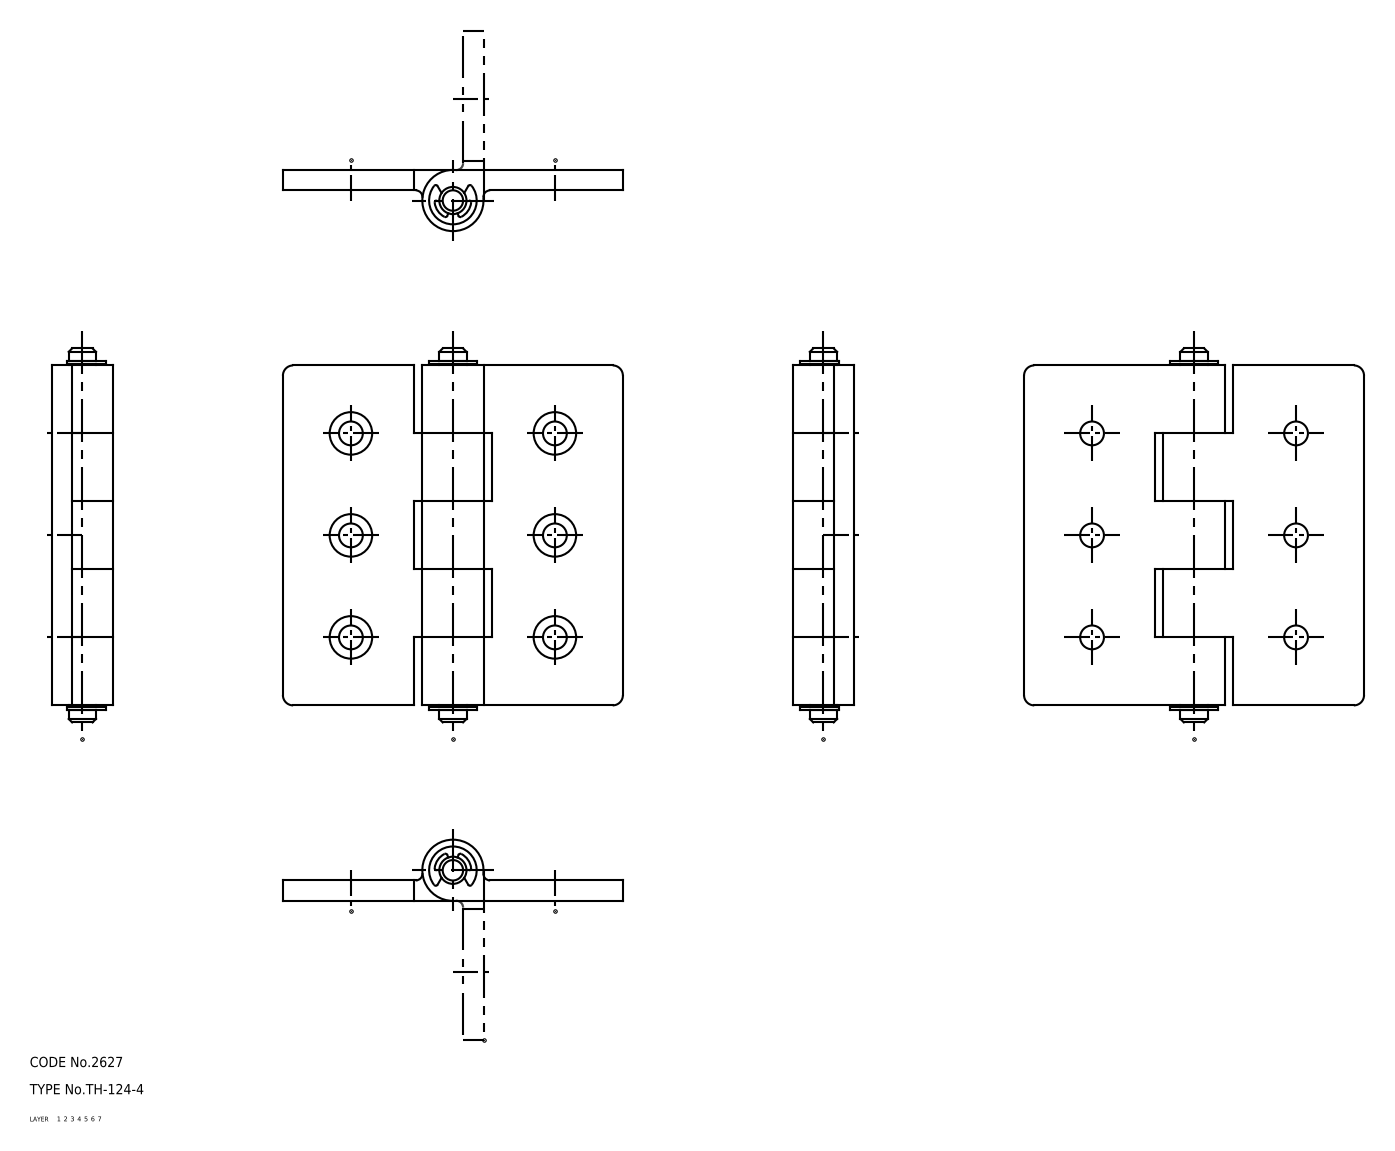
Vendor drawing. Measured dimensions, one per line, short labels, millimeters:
name: 67116428; 67116441; 67116454; 67116467 (+1 more)
written by: CADfix (AUTOMOTIVE_DESIGN)
unit: mm
bodies: 5 solids, 131 faces (0 planar, 0 cylindrical, 131 other)
size: 110 × 100 × 18
volume: 73 440 mm³; area: 32 288 mm²
